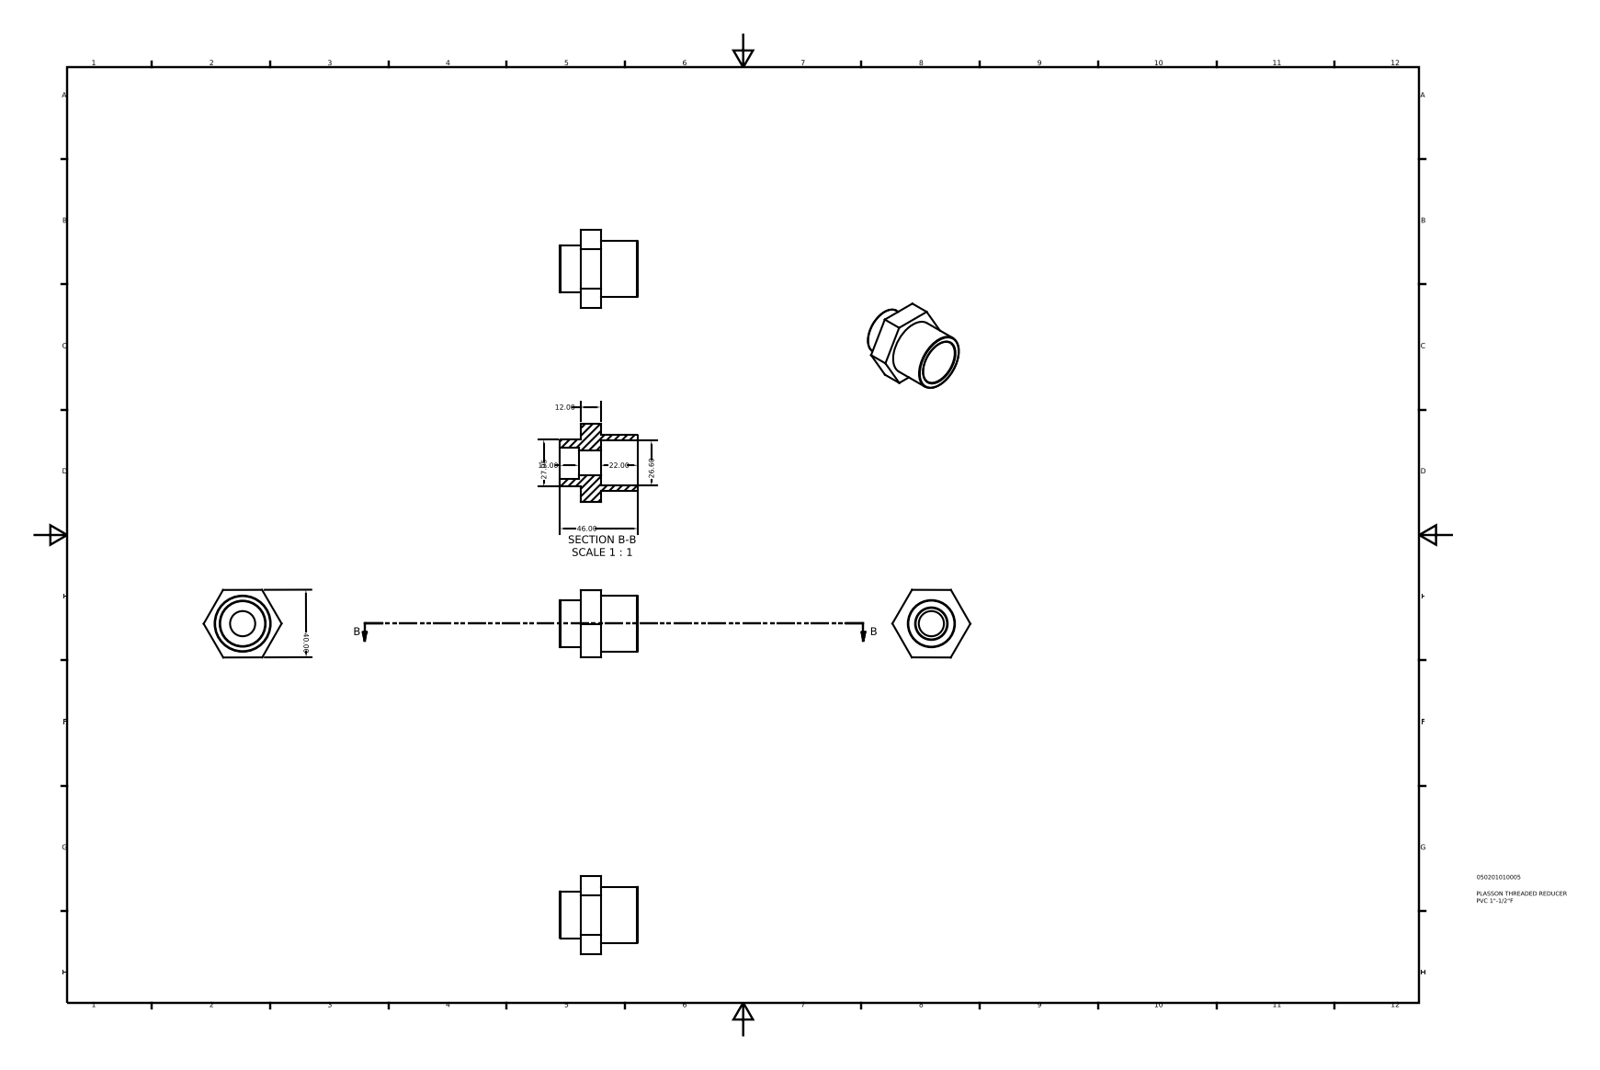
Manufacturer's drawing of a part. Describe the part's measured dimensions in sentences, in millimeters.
The part is named "050201010005". Its 3-D file was written by "Autodesk Inventor 2015 (AUTOMOTIVE_DESIGN)". It is 1 solid with 21 faces: 12 planar, 5 cylindrical and 4 other. Overall it measures 46.19 by 46 by 40.07 millimeters. Its volume is 25 590 cubic millimeters and its surface area 10 480 square millimeters. Round holes: 1 of diameter 14.9, 1 of diameter 18.63, 1 of diameter 26.6. Round bosses or shafts: 1 of diameter 33.25, 1 of diameter 27.95. The main face-to-face distances are 12, 40.02, 24, 40, 46, 34, 22, 11, 1, 13.
